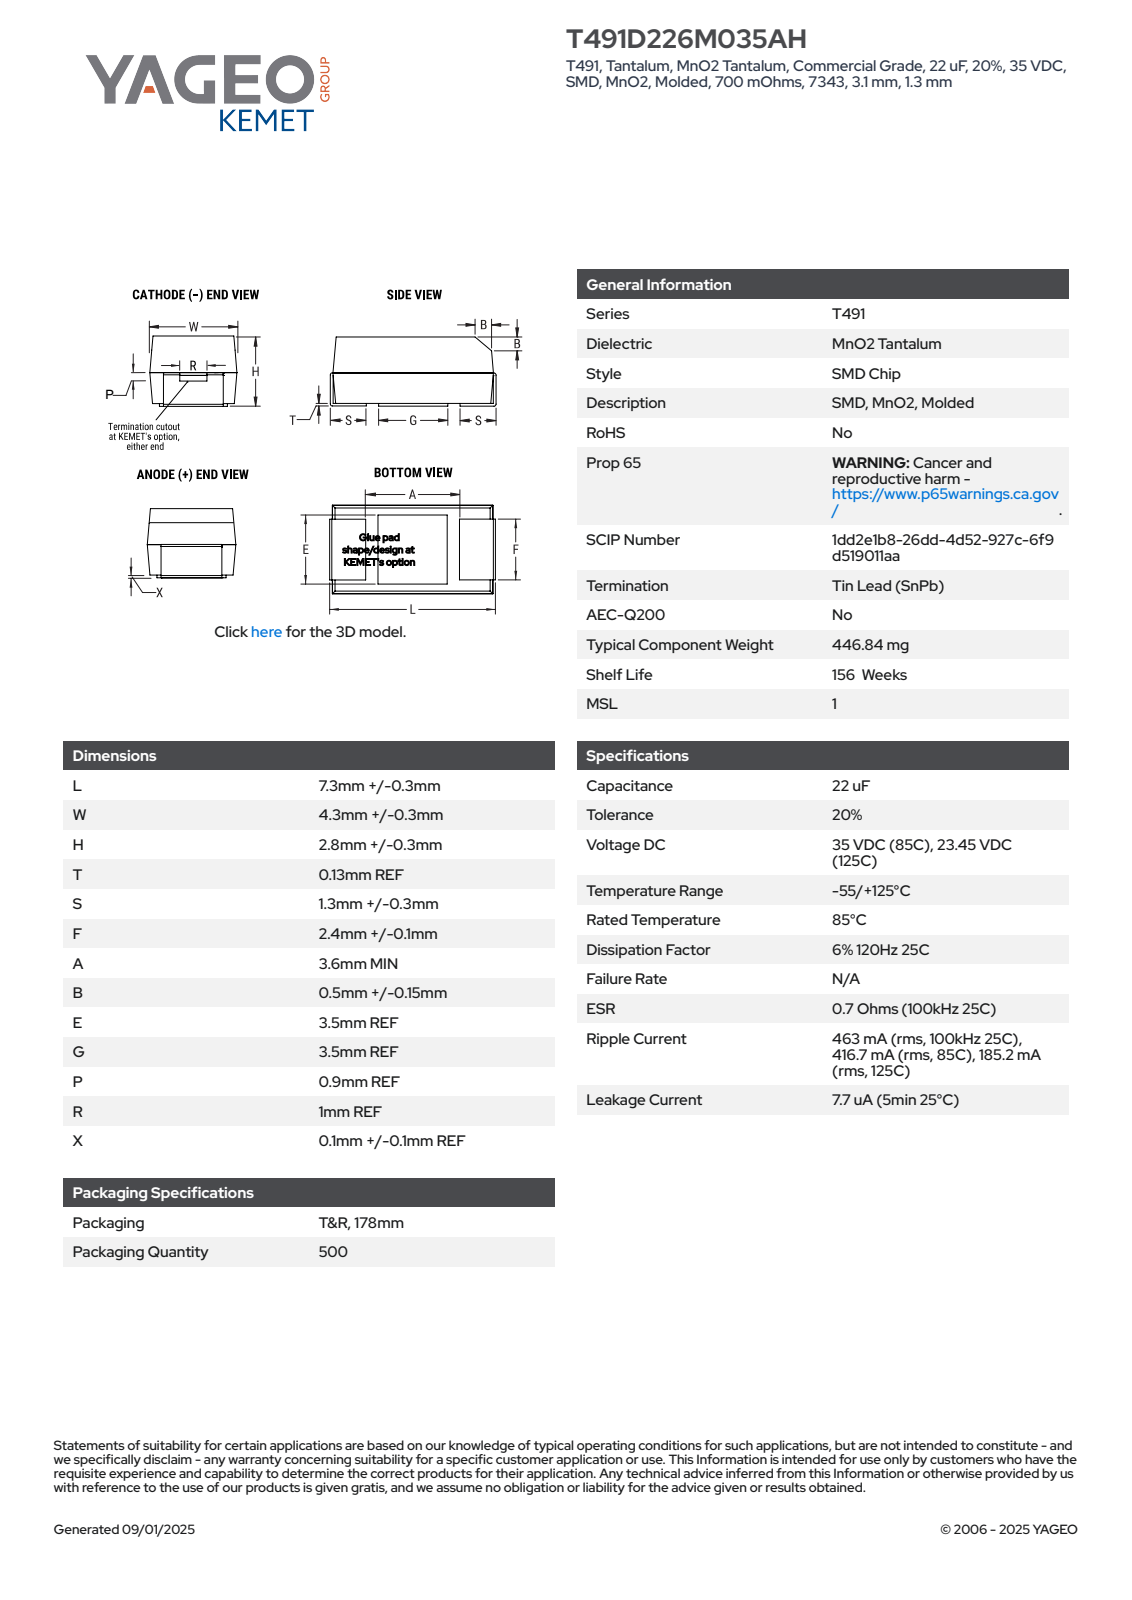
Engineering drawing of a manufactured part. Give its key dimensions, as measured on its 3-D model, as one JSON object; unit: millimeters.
{"part_name": "CTSM_TCM2NK_7343_L7.6W4.6H3.1T0.13S1.3F2.5A3.6B0.65E3.5G3.5P0.9R1X0.2", "step_written_by": "SolidWorks 2020 (AUTOMOTIVE_DESIGN)", "units": "millimeters", "bodies": {"solids": 4, "faces": 100, "planar": 95, "cylindrical": 5, "other": 0}, "overall_size": [7.6, 4.6, 3.1], "volume_mm3": 93, "surface_area_mm2": 153, "partial_cylinders_radius": [[0.1, 4]], "face_to_face_distances": [3.1, 2.9, 4.54, 4.53, 2.97, 7.47, 7.6, 7.34, 2.05, 5.55]}
